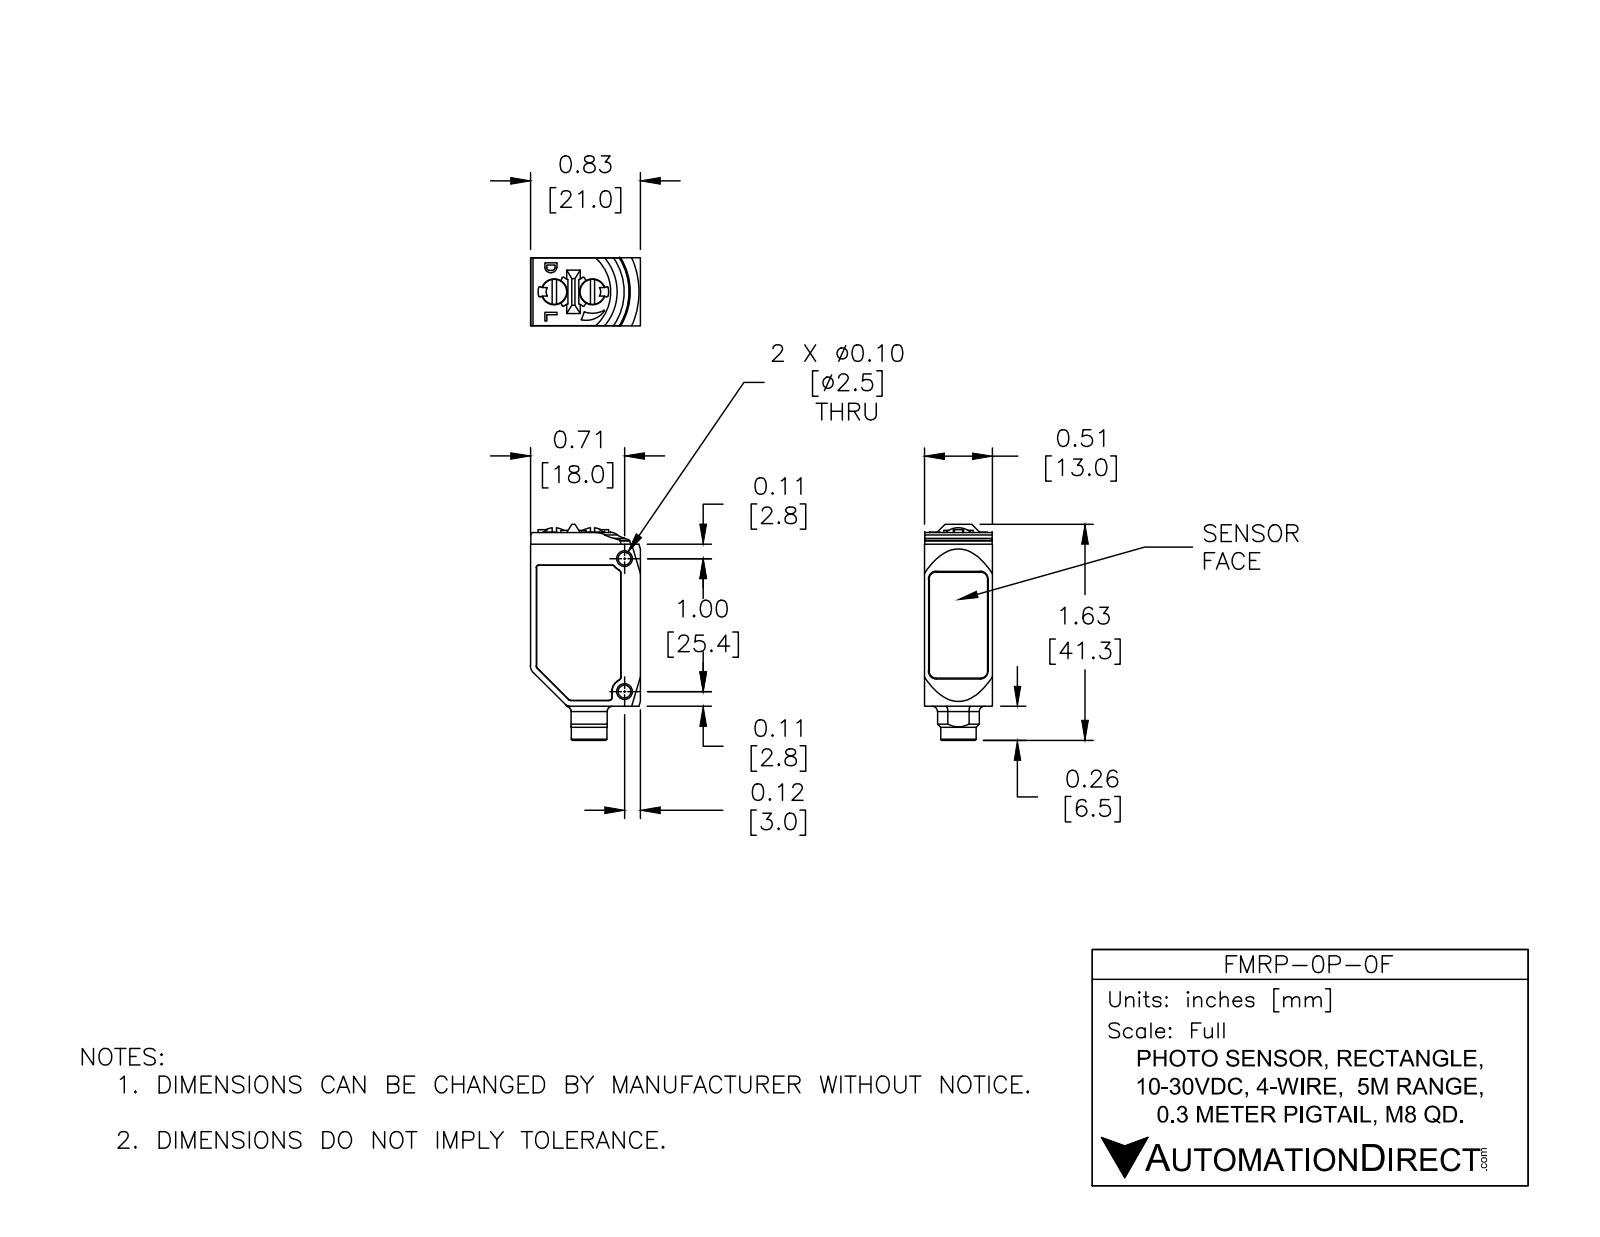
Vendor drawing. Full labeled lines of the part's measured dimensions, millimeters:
Part name (STEP PRODUCT): FMRP-0P-0F
STEP written by: SolidWorks 2017 (AUTOMOTIVE_DESIGN)
Units: millimetres
Bodies: 1 solid, 197 faces (89 planar, 79 cylindrical, 29 other)
Overall size (bounding box): 41.3 × 21 × 13
Volume: 8 640 mm³ · Surface area: 3 394 mm²
Round holes (diameter × count): ⌀2.5 ×2, ⌀5 ×2, ⌀5.8 ×1
Round bosses / shafts (diameter × count): ⌀4.8 ×2, ⌀6.8 ×1
Partial cylindrical surfaces — rounded edges, fillets, slot ends (radius × count): R0.5 ×7, R0.5 ×7, R1 ×5, R0.2 ×4, R0.3 ×4, R1.3 ×4, R1.5 ×4, R0.1 ×3
Main face-to-face distances: 13, 21, 33.2, 13, 0.8, 12.2, 0.9, 0.9, 12, 0.8
Hole centre spacings: 0.7, 6.7, 7.3, 25.4
